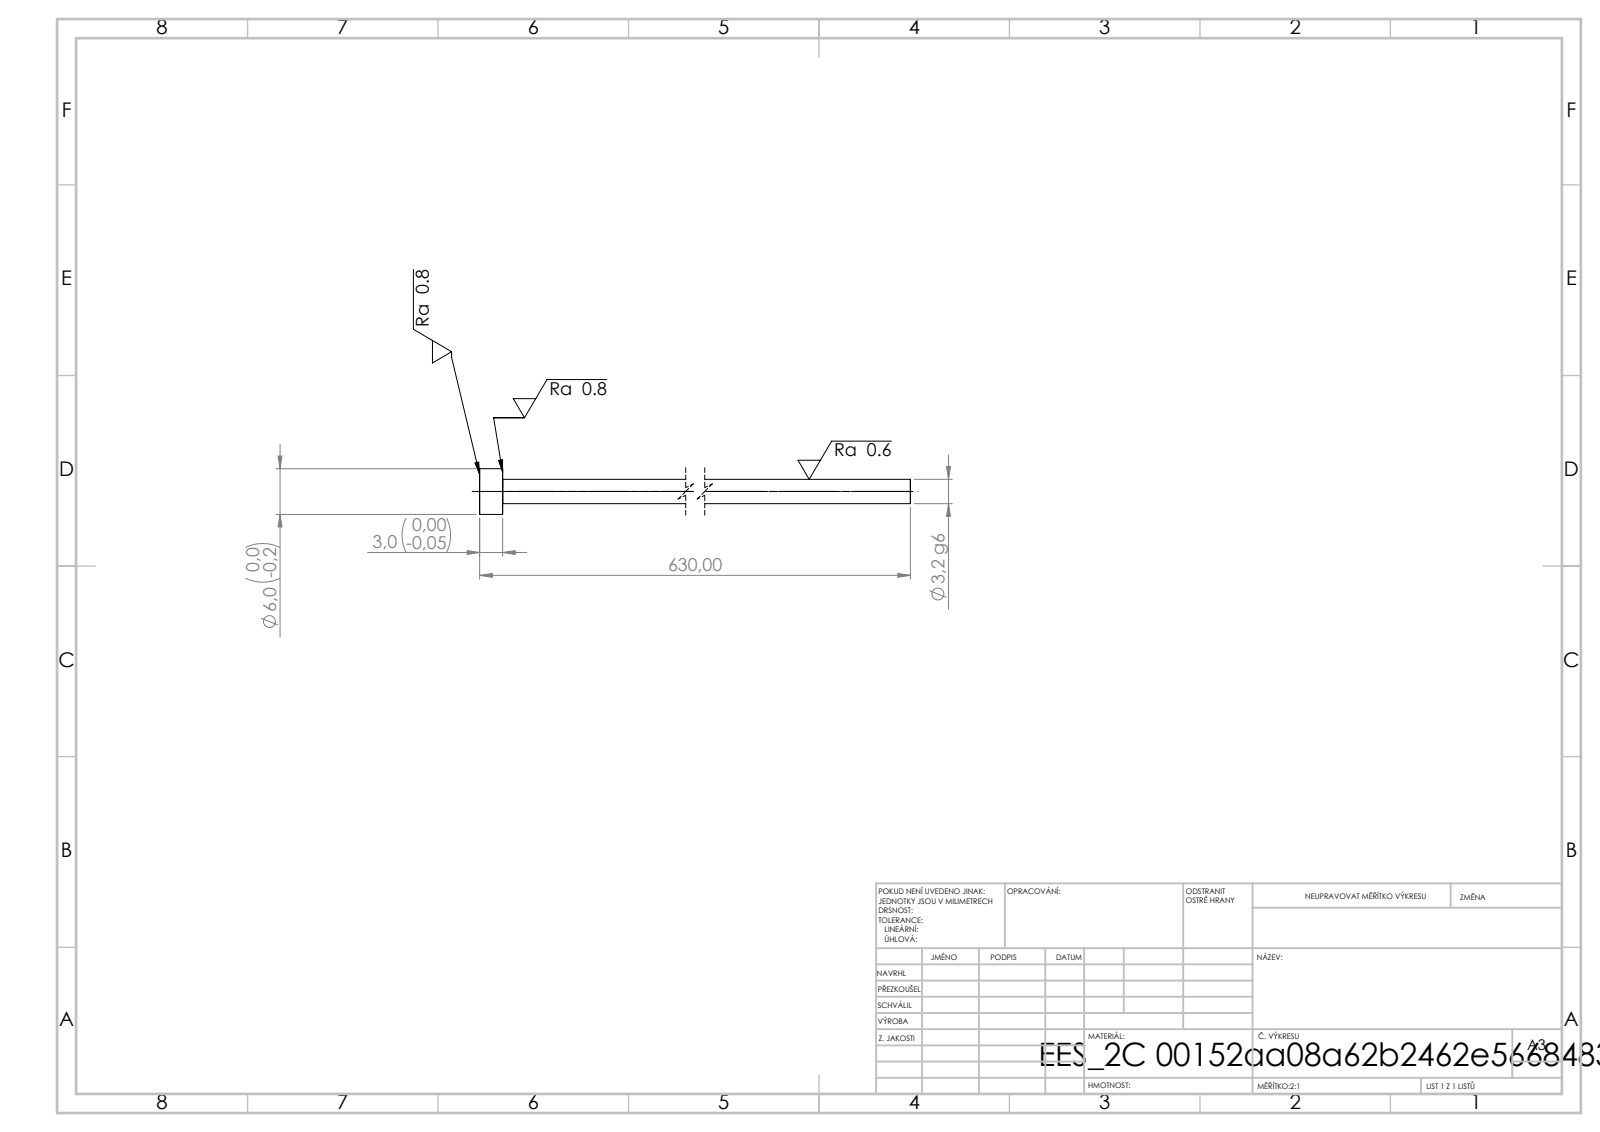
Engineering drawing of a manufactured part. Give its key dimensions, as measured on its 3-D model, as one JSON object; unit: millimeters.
{"step_written_by": "SolidWorks 2019 (CONFIG_CONTROL_DESIGN)", "units": "millimeters", "bodies": {"solids": 1, "faces": 7, "planar": 3, "cylindrical": 4, "other": 0}, "overall_size": [630, 6, 6], "volume_mm3": 5127, "surface_area_mm2": 6416, "round_bosses_or_shafts": [[6, 1], [3.2, 1]], "face_to_face_distances": [3, 630, 627]}
